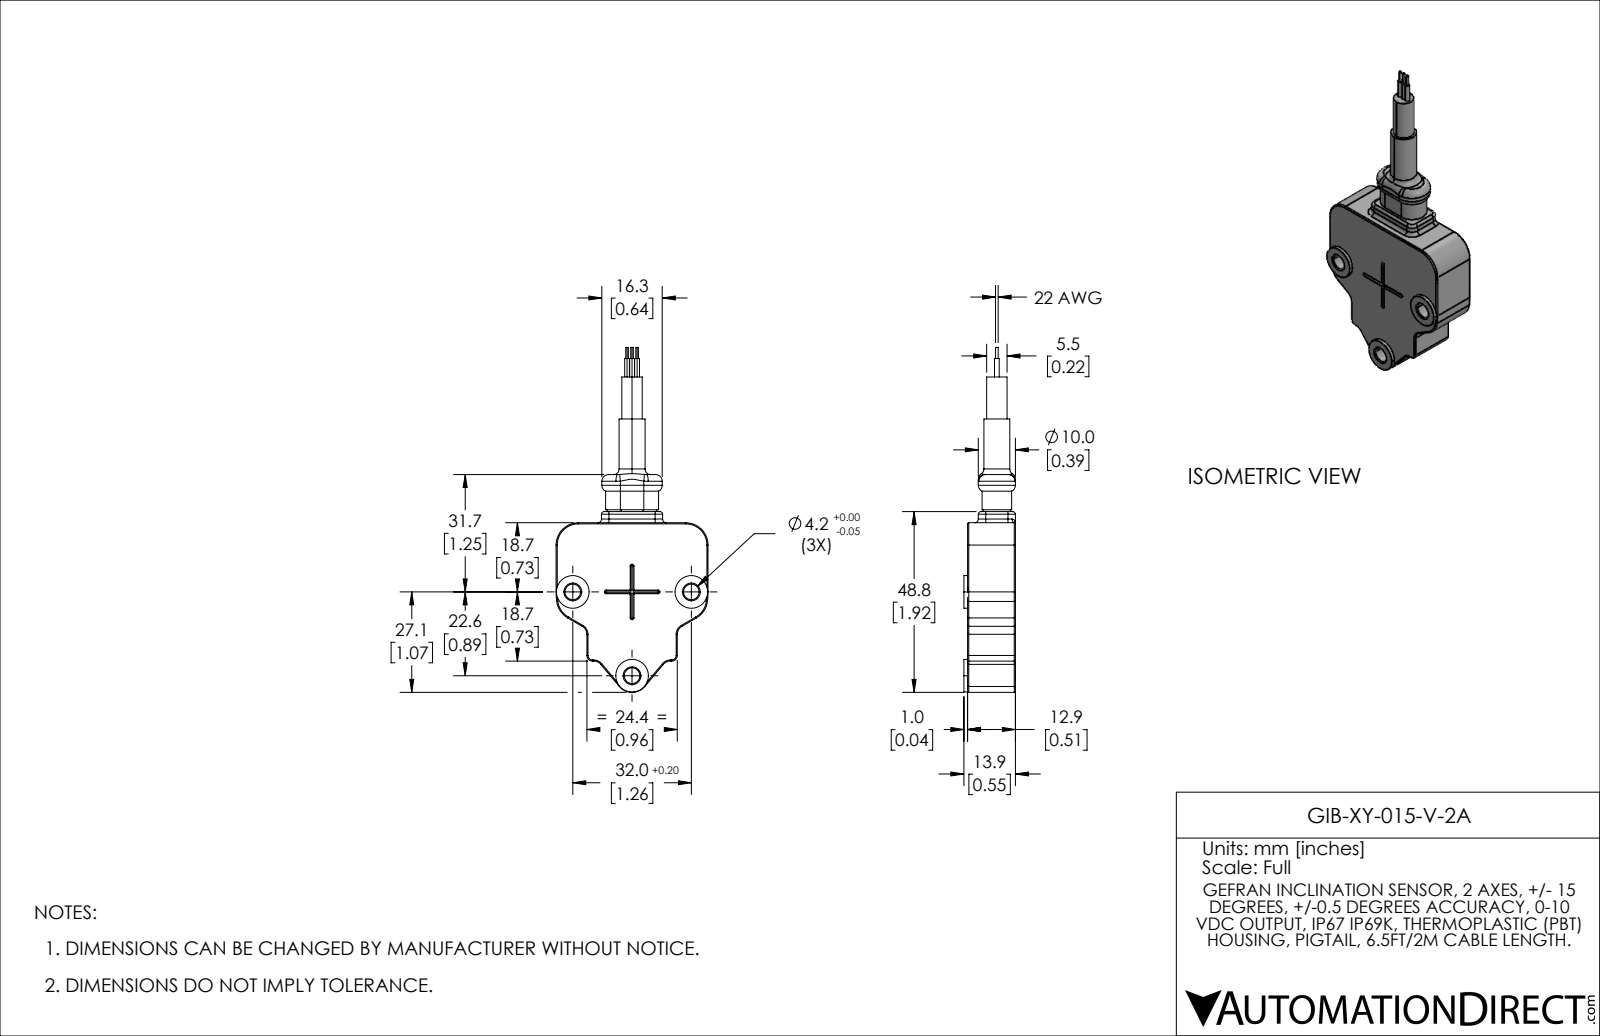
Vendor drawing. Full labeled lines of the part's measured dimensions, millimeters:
Part name (STEP PRODUCT): GIB-XY-015-V-2A
STEP written by: SolidWorks 2021 (AUTOMOTIVE_DESIGN)
Units: millimetres
Bodies: 1 solid, 201 faces (47 planar, 87 cylindrical, 67 other)
Overall size (bounding box): 93 × 41 × 13.9
Volume: 20 420 mm³ · Surface area: 6 435 mm²
Round holes (diameter × count): ⌀4.2 ×3
Round bosses / shafts (diameter × count): ⌀8.8 ×3, ⌀1.3 ×3, ⌀0.7 ×3, ⌀7 ×1, ⌀5.5 ×1
Partial cylindrical surfaces — rounded edges, fillets, slot ends (radius × count): R0.3 ×20, R0.2 ×4, R0.7 ×4, R2 ×4, R2.5 ×4, R6 ×4, R1 ×3, R1.5 ×2
Main face-to-face distances: 12.9, 1, 41, 8.3, 32.7, 13.9, 24.4, 9, 3.9, 3
Hole centre spacings: 27.7, 32
